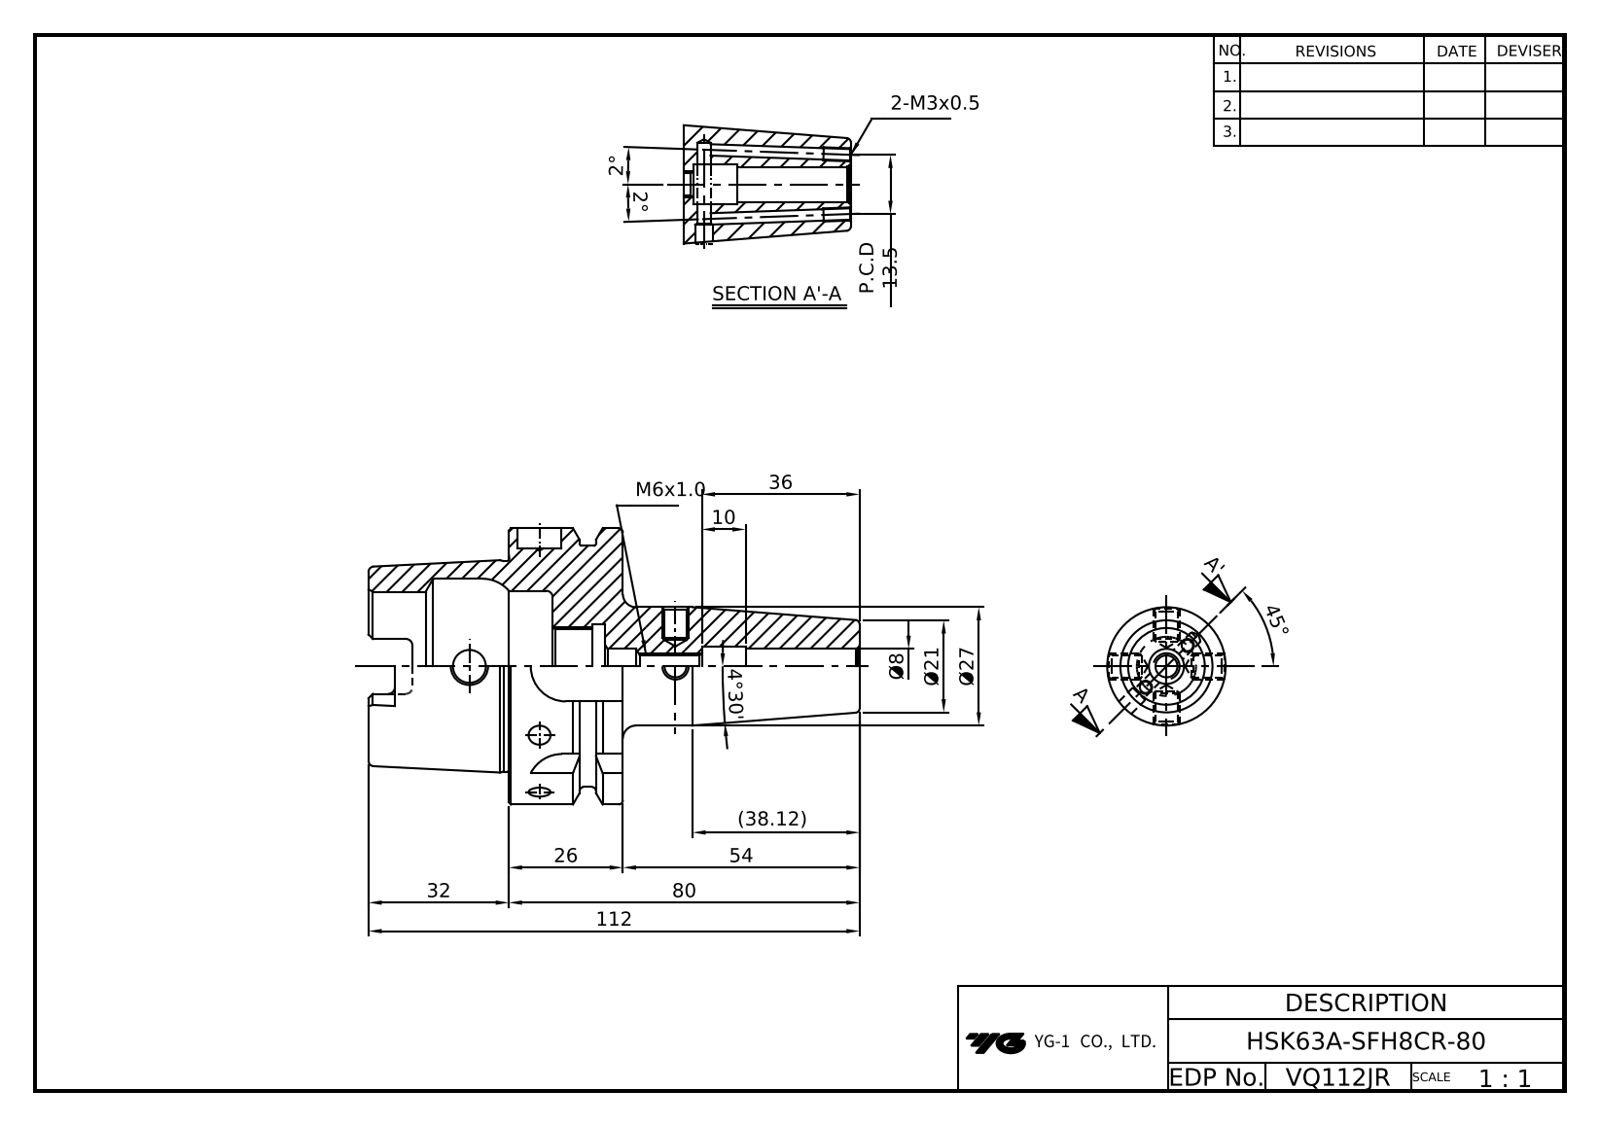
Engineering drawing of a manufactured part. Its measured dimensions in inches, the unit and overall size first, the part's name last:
Units: inches
Overall size (bounding box): 4.409 × 2.48 × 2.48
Round holes (diameter × count): ⌀0.097 ×2, ⌀0.194 ×1, ⌀0.295 ×1, ⌀0.315 ×1, ⌀0.362 ×1, ⌀0.394 ×1, ⌀0.666 ×1, ⌀0.748 ×1, ⌀1.339 ×1, ⌀1.575 ×1
Round bosses / shafts (diameter × count): ⌀2.48 ×1, ⌀2.165 ×1, ⌀1.891 ×1, ⌀1.063 ×1
Partial cylindrical surfaces — rounded edges, fillets, slot ends (radius × count): R0.059 ×6, R0.113 ×4, R0.315 ×4
Main face-to-face distances: 1.024, 0.394, 0.63, 2.283, 1.26, 2.126, 1.654, 0.866, 2.087, 0.157
Volume: 6.426 in³ · Surface area: 43.4 in²
Bodies: 1 solid, 121 faces (42 planar, 36 cylindrical, 43 other)
Part name (STEP PRODUCT): LO-HSK63A-SFH8CR-80
STEP written by: Autodesk Inventor 2022 (AUTOMOTIVE_DESIGN)
